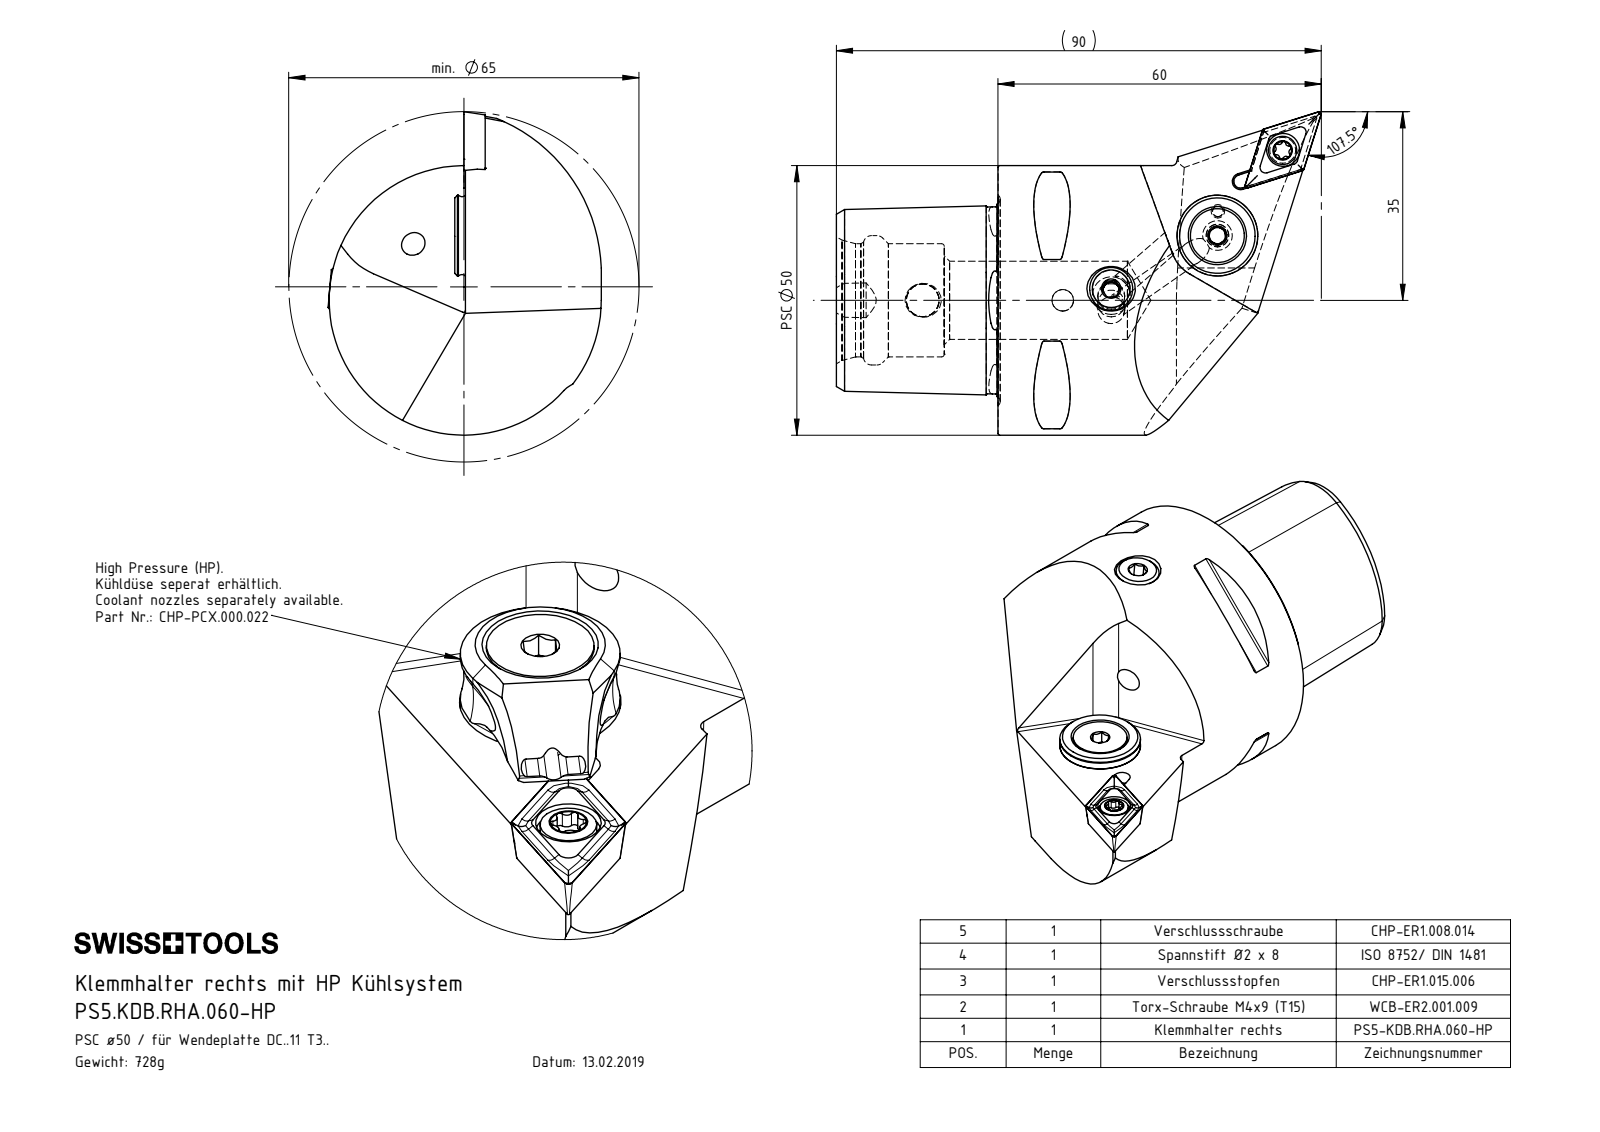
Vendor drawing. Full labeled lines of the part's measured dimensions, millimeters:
Part name (STEP PRODUCT): WCB-ER2.001.009_A; CHP-ER1.015.006; PS5-KDB.RHA.060-HP_C; DIN 3771 - 13x1 (+6 more)
STEP written by: SolidWorks 2017 (AUTOMOTIVE_DESIGN)
Units: millimetres
Bodies: 8 solids, 373 faces (90 planar, 98 cylindrical, 185 other)
Overall size (bounding box): 90.01 × 60 × 50.71
Volume: 92 319 mm³ · Surface area: 21 292 mm²
Round holes (diameter × count): ⌀4.2 ×3, ⌀6.1 ×2, ⌀1.2 ×1, ⌀2 ×1, ⌀2.5 ×1, ⌀3 ×1, ⌀3.3 ×1, ⌀4 ×1, ⌀4.4 ×1, ⌀5 ×1, ⌀5.2 ×1, ⌀7 ×1
Round bosses / shafts (diameter × count): ⌀50 ×1, ⌀15 ×1, ⌀13.4 ×1, ⌀10 ×1, ⌀8 ×1, ⌀5.5 ×1, ⌀5.25 ×1, ⌀5 ×1
Partial cylindrical surfaces — rounded edges, fillets, slot ends (radius × count): R0.5 ×10, R0.34 ×6, R0.59 ×6, R1.25 ×1, R4 ×1, R7 ×1, R25.5 ×1, R31 ×1
Main face-to-face distances: 30, 4.5, 19.18, 0.83, 3.67, 44.4, 10, 20, 20.7, 21.53
Hole centre spacings: 4.5, 16.52, 16.65, 19.92, 20.04, 26, 31.13, 33.19
